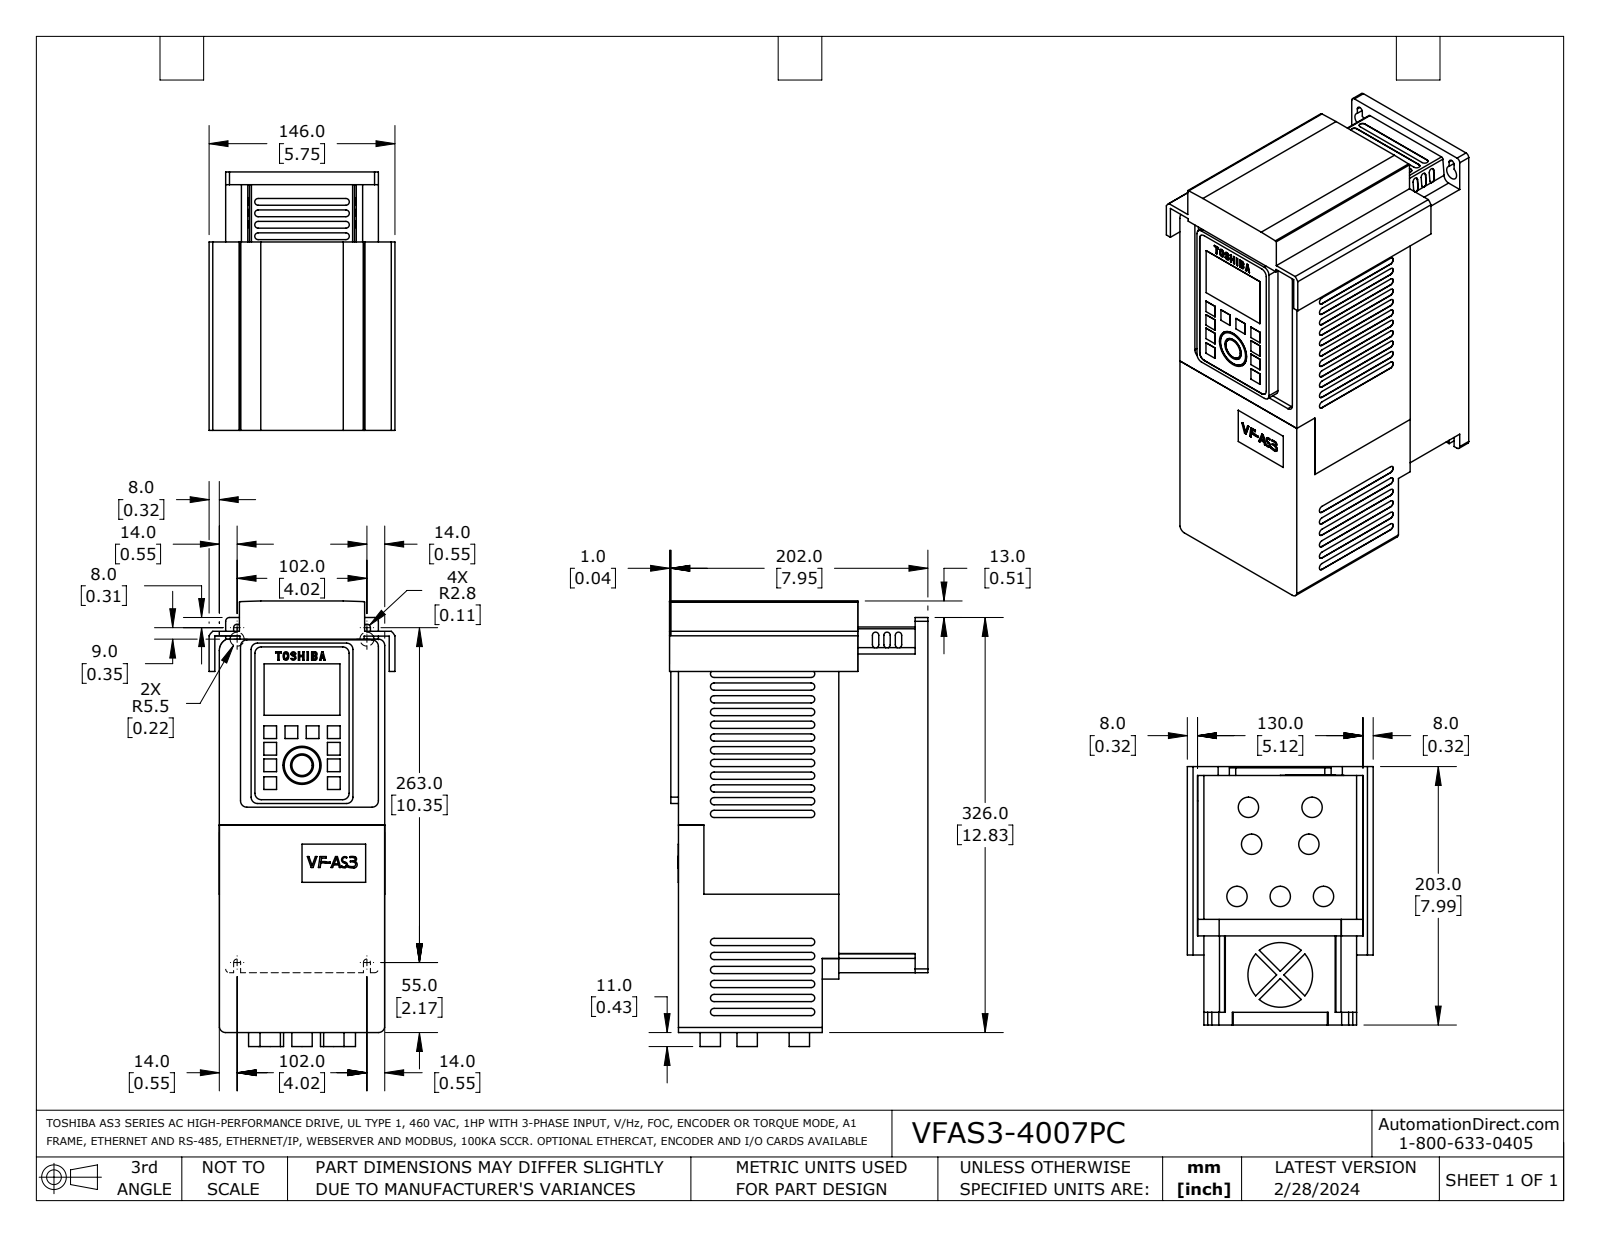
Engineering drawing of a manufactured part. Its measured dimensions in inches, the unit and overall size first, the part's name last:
Units: inches
Overall size (bounding box): 13.763 × 7.992 × 5.663
Round holes (diameter × count): ⌀0.433 ×2, ⌀0.63 ×1, ⌀1.102 ×1, ⌀2.001 ×1
Round bosses / shafts (diameter × count): ⌀0.63 ×7, ⌀1.181 ×1, ⌀0.709 ×1
Partial cylindrical surfaces — rounded edges, fillets, slot ends (radius × count): R0.112 ×48, R0.197 ×17, R0.105 ×8, R0.039 ×5, R0.078 ×5, R0.108 ×4, R0.118 ×4, R0.394 ×4
Main face-to-face distances: 0.197, 4.921, 0.118, 7.717, 5.114, 0.193, 4.917, 4.724, 5.108, 0.187
Hole centre spacings: 4.388, 4.016
Volume: 461.5 in³ · Surface area: 530.5 in²
Bodies: 2 solids, 693 faces (442 planar, 235 cylindrical, 16 other)
Part name (STEP PRODUCT): VFAS3-4007PC
STEP written by: SolidWorks 2021 (AUTOMOTIVE_DESIGN)
